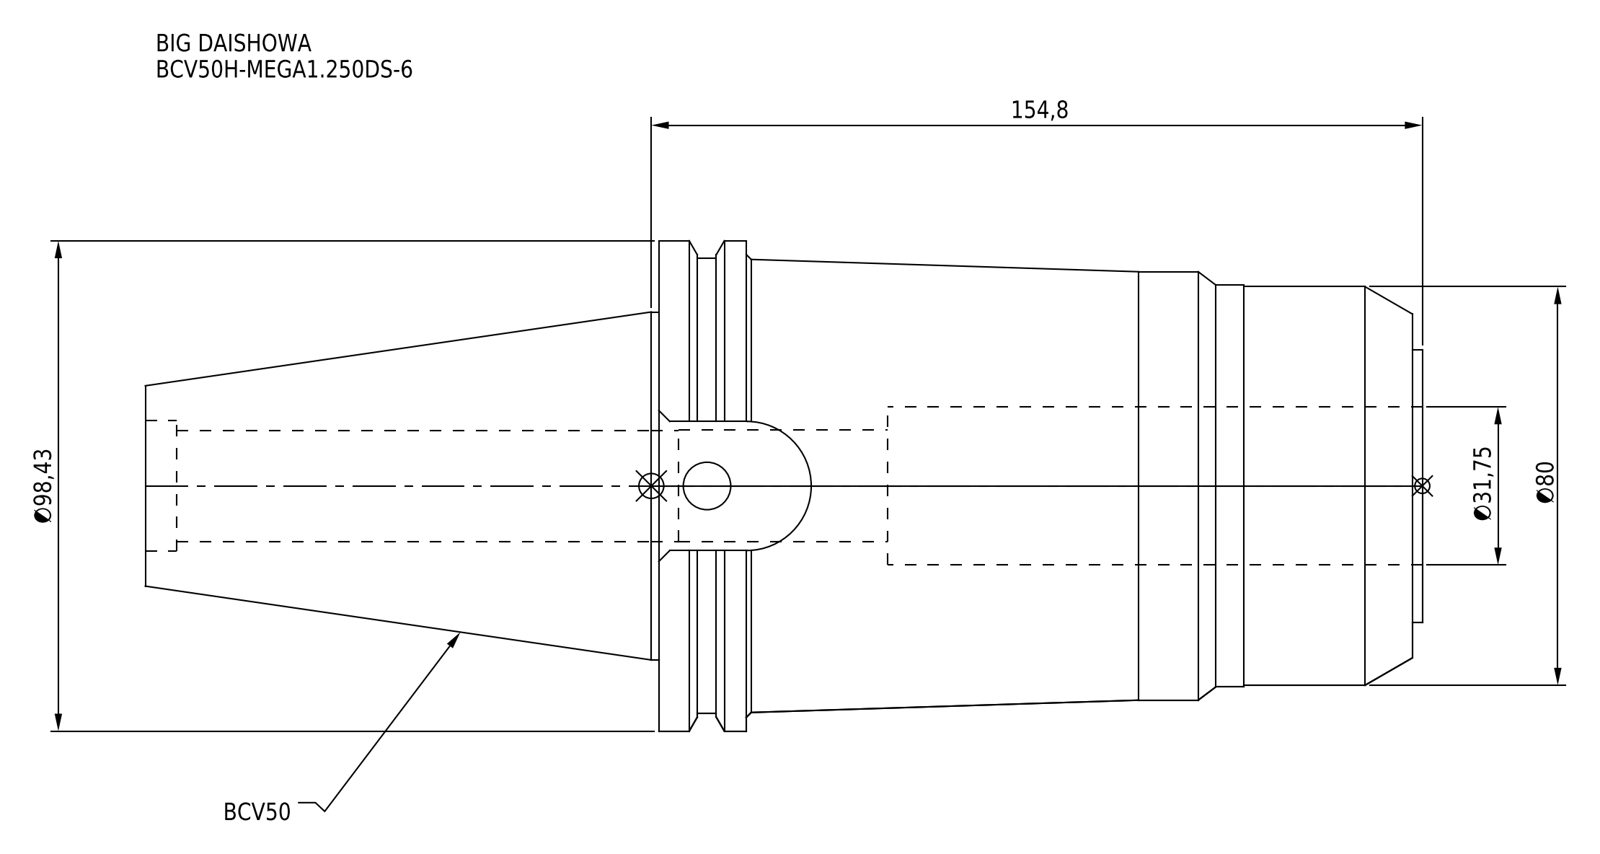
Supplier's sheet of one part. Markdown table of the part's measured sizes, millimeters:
| quantity | value |
| --- | --- |
| part name | BCV50H-MEGA1_250DS-6 |
| STEP written by | CREO PARAMETRIC BY PTC INC, 2016380 (AUTOMOTIVE_DESIGN) |
| units | millimeters |
| bodies | 1 solid, 69 faces (25 planar, 30 cylindrical, 14 other) |
| overall size | 256.4 × 98.42 × 94.95 |
| volume | 993 171 mm³ |
| surface area | 92 101 mm² |
| round holes (diameter × count) | 9.53 × 1, 22.3 × 1, 22.5 × 1, 26.23 × 1, 31.75 × 1 |
| round bosses / shafts (diameter × count) | 98.42 × 1, 91.29 × 1, 86 × 1, 80.7 × 1, 80 × 1, 69.85 × 1, 54.7 × 1 |
| partial cylindrical surfaces (radius × count) | 12.96 × 1 |
| main face-to-face distances | 153.3, 2, 151.3, 256.4, 254.4, 103.1, 135.75, 133.75, 17.55, 120.65 |
